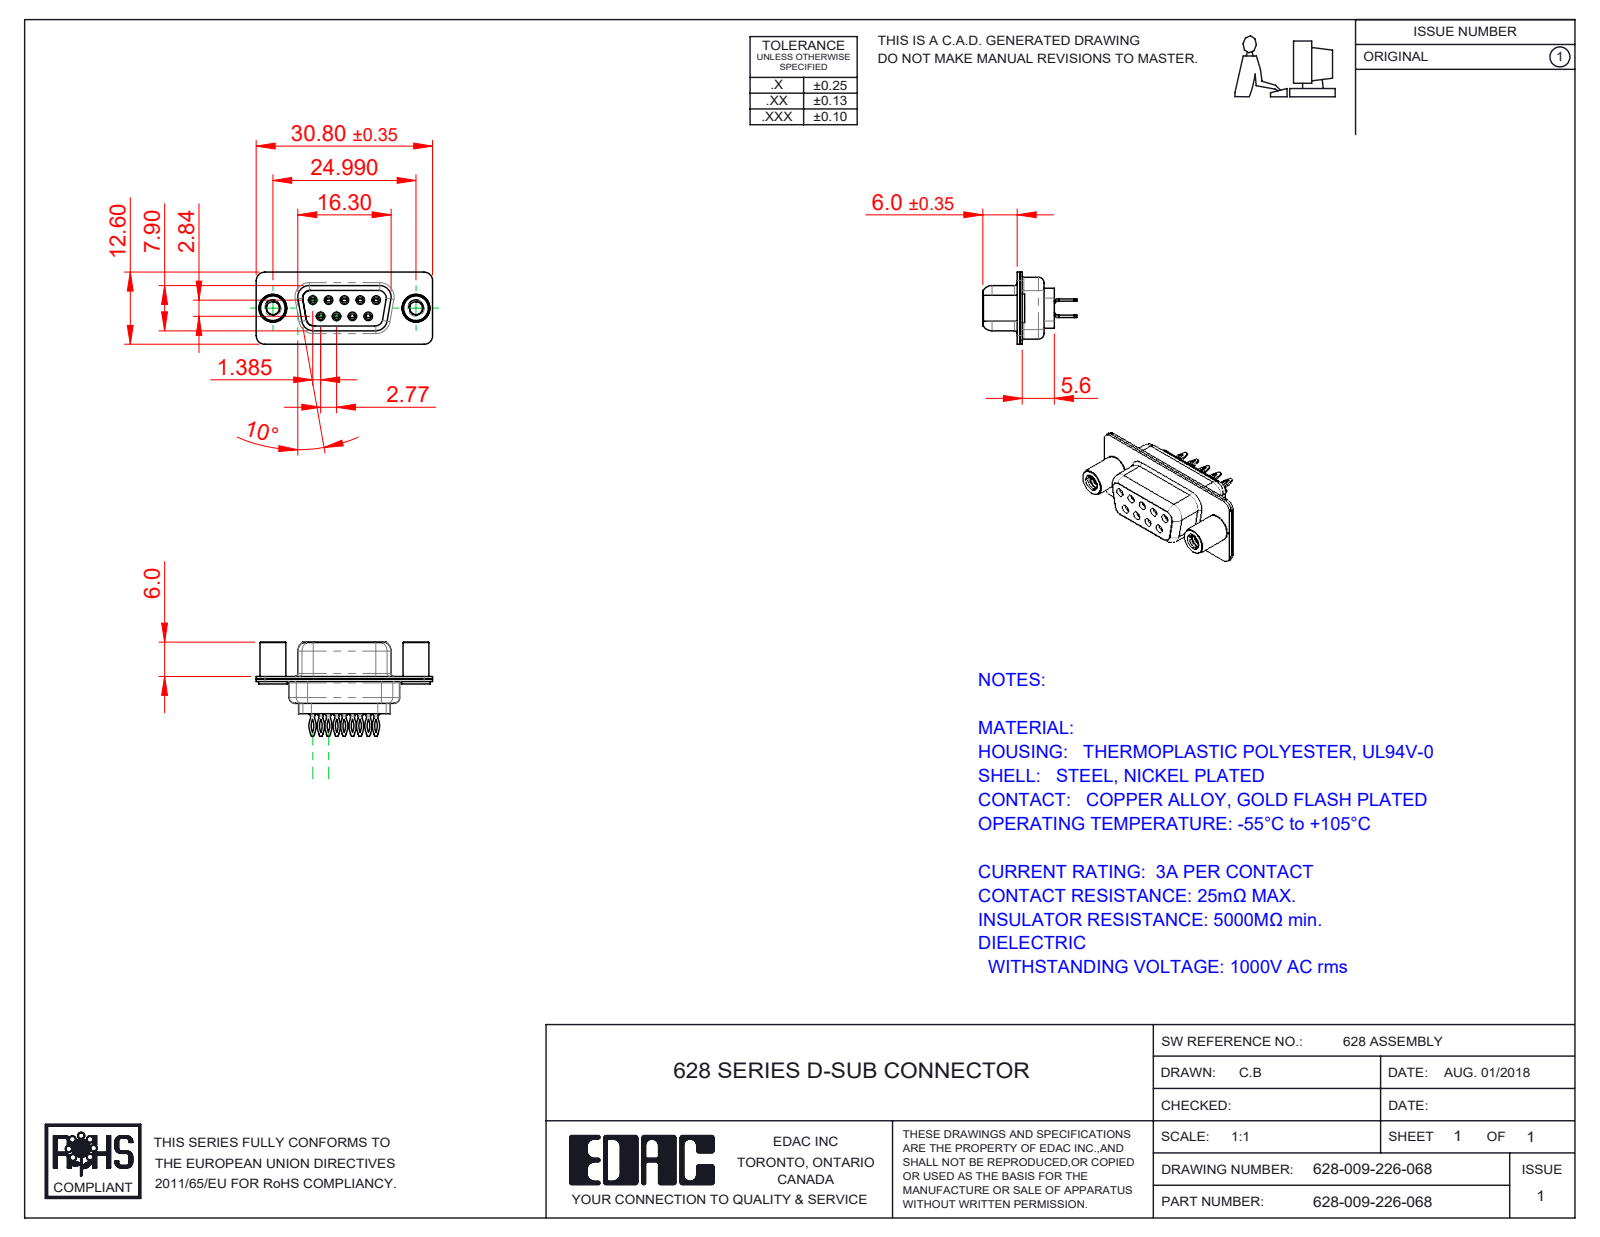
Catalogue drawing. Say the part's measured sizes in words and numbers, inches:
The part is named "628 Shell Front_09 Contacts; 628 4-40 Threaded Standoff; 628 Housing_09 LP; 628 Contact Row 2_26L (+3 more)". Its 3-D file was written by "SolidWorks 2020 (CONFIG_CONTROL_DESIGN)". It is 14 solids with 1222 faces: 312 planar, 408 cylindrical and 502 other. Overall it measures 1.213 by 0.648 by 0.496 inches. Its volume is 0.111 cubic inches and its surface area 7.249 square inches. Round holes: 9 of diameter 0.031, 9 of diameter 0.035, 9 of diameter 0.043, 9 of diameter 0.063, 5 of diameter 0.067, 2 of diameter 0.089, 2 of diameter 0.157, 2 of diameter 0.159, 2 of diameter 0.191. Round bosses or shafts: 9 of diameter 0.079, 9 of diameter 0.059, 9 of diameter 0.047, 2 of diameter 0.197, 2 of diameter 0.195, 2 of diameter 0.189, 2 of diameter 0.177. Partial cylindrical surfaces (rounded edges, fillets, slot ends): 18 of radius 0.115, 18 of radius 0.131, 17 of radius 0.059, 12 of radius 0.079, 9 of radius 0.011, 6 of radius 0.053, 4 of radius 0.01, 4 of radius 0.02. The main face-to-face distances are 0.018, 0.016, 0.035, 0.075, 0.335, 0.26, 0.055, 0.033, 0.071, 0.02. The hole center spacings are 0.124, 0.109, 0.218, 0.198, 0.198, 0.327, 0.294, 0.295.
